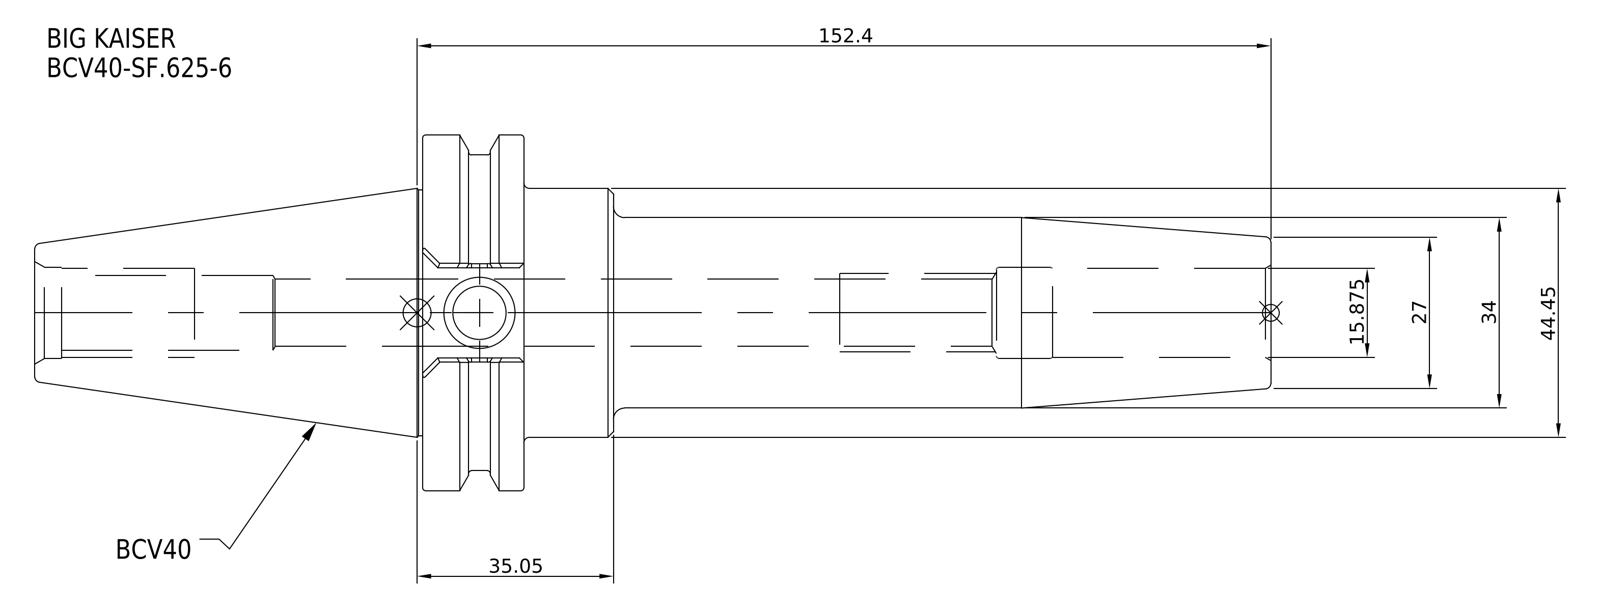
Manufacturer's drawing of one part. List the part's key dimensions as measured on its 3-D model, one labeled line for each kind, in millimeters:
Part name (STEP PRODUCT): BCV40-SF_625-6
STEP written by: SolidWorks 2021 (CONFIG_CONTROL_DESIGN)
Units: millimetres
Bodies: 1 solid, 30 faces (8 planar, 14 cylindrical, 8 other)
Overall size (bounding box): 220.65 × 63.5 × 63.5
Volume: 236 739 mm³ · Surface area: 33 156 mm²
Round holes (diameter × count): ⌀15.88 ×1
Round bosses / shafts (diameter × count): ⌀63.5 ×1, ⌀56.36 ×1, ⌀44.45 ×1, ⌀34 ×1
Main face-to-face distances: 18.05, 16, 34.05, 103.3, 87.3, 69.25, 117.35, 133.35, 151.4, 220.65
